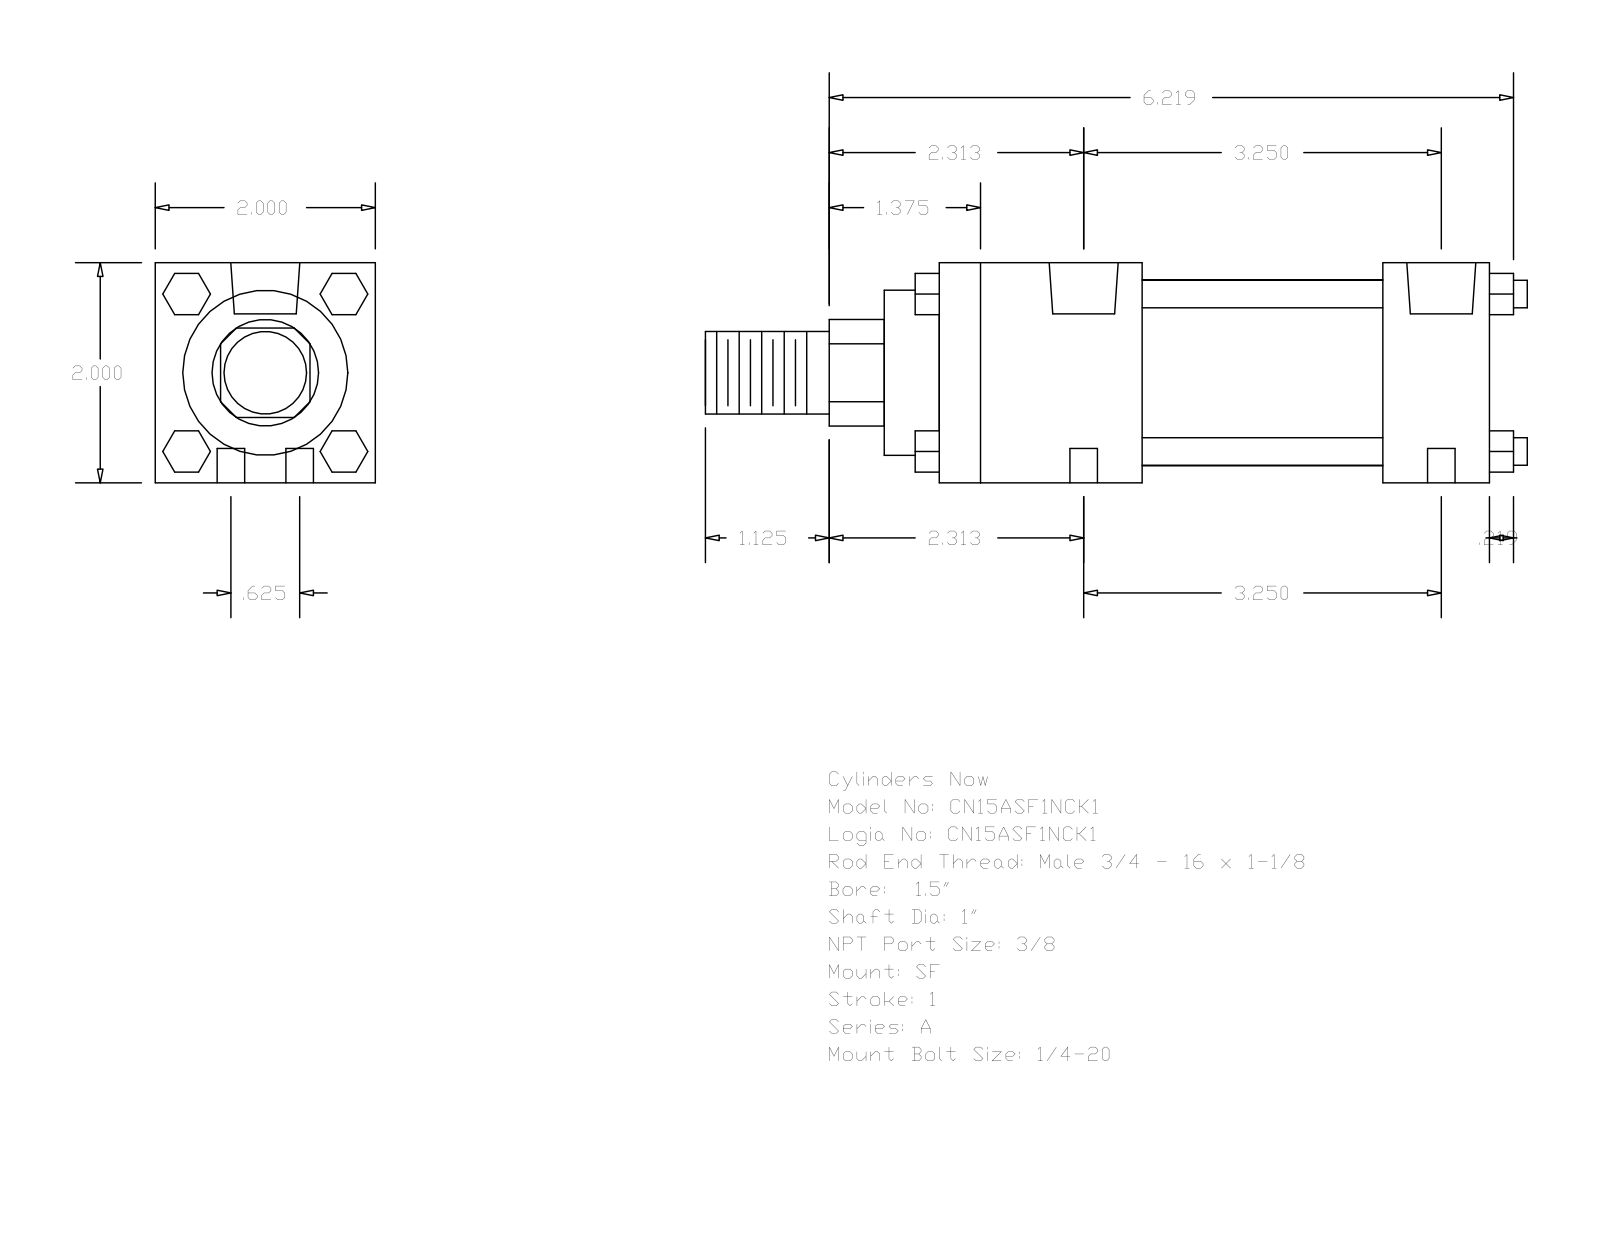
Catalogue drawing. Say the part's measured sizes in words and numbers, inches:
The part is named "A_SF__0150_1". Its 3-D file was written by "GSSL Pune (CONFIG_CONTROL_DESIGN)". It is 0 solids with 124 faces: 94 planar, 30 cylindrical and 0 other. Overall it measures 7.469 by 2 by 2 inches. Round holes: 4 of diameter 0.25, 2 of diameter 0.219, 2 of diameter 0.627. Round bosses or shafts: 4 of diameter 0.25, 1 of diameter 1.69, 1 of diameter 1.5, 1 of diameter 1, 1 of diameter 0.75. Partial cylindrical surfaces (rounded edges, fillets, slot ends): 1 of radius 0.484. The main face-to-face distances are 2, 5, 1.844, 4.031, 2.187, 3.156, 0.969, 0.5, 2.344, 4.531. The hole center spacings are 0.313, 3.265, 3.25, 0.625, 3.309, 2.937.
